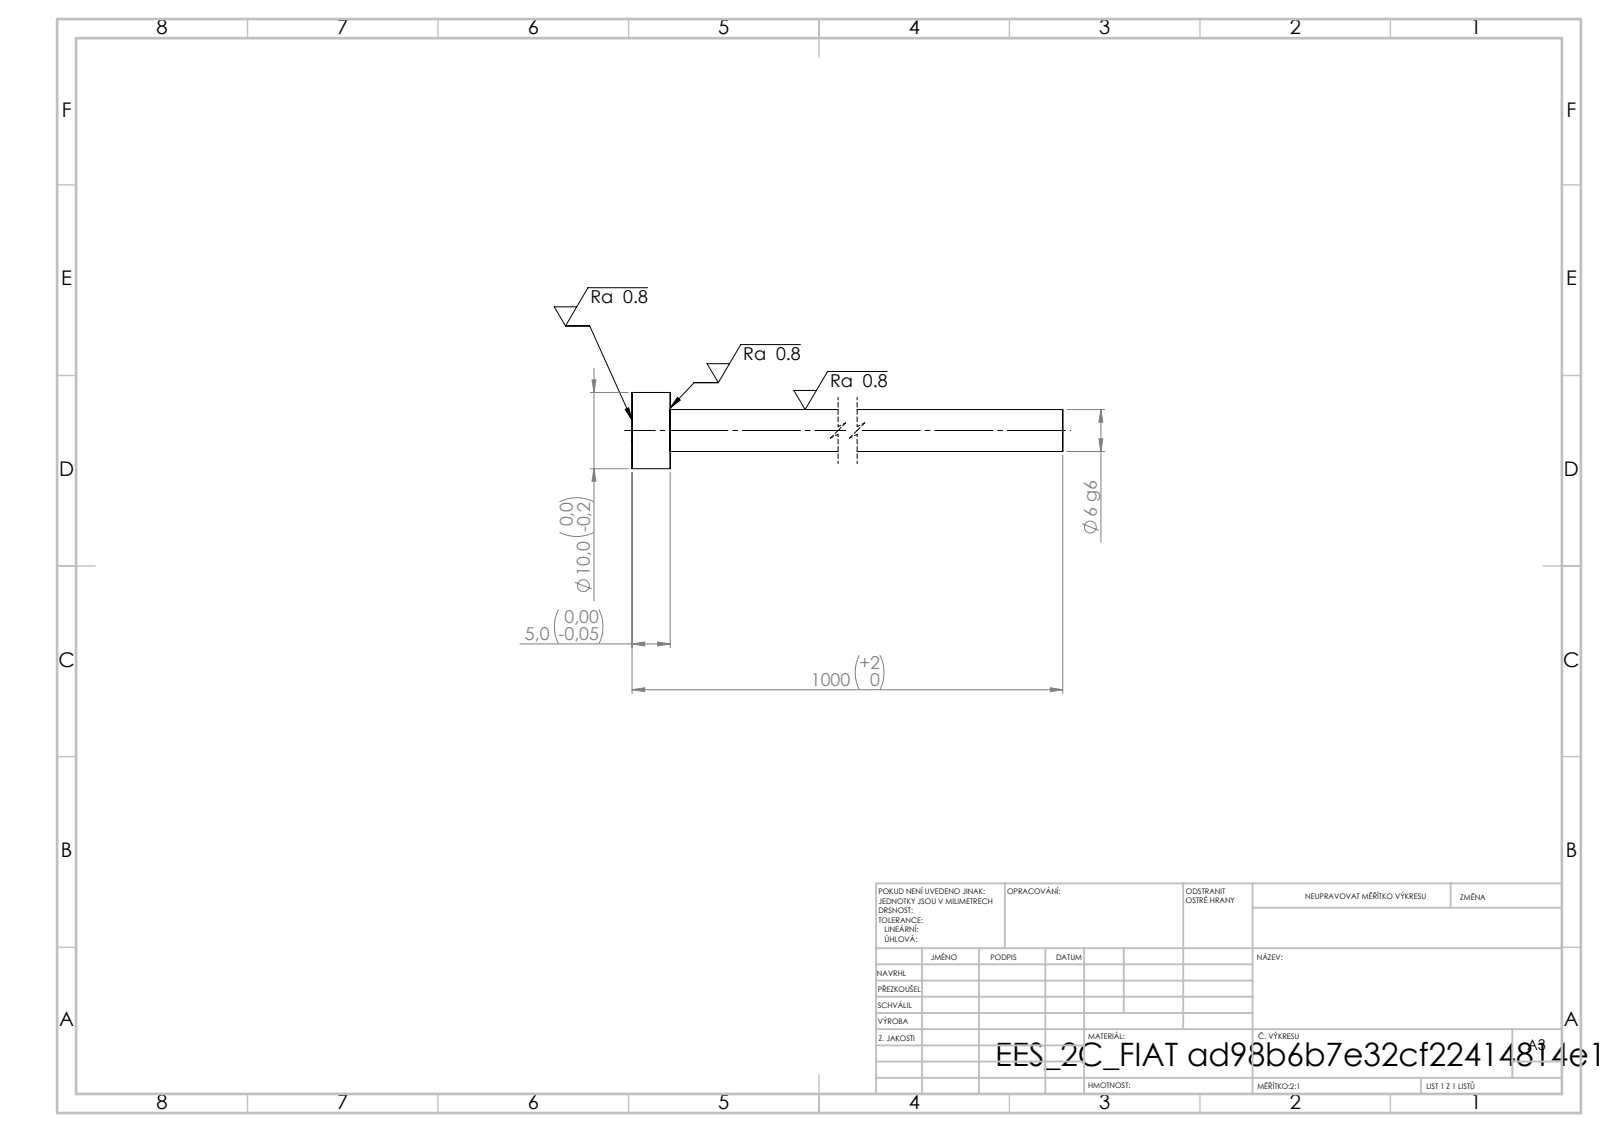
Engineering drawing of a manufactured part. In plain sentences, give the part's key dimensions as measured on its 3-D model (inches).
Its 3-D file was written by "SolidWorks 2019 (CONFIG_CONTROL_DESIGN)". It is 1 solid with 7 faces: 3 planar, 4 cylindrical and 0 other. Overall it measures 39.37 by 0.394 by 0.394 inches. Its volume is 1.467 cubic inches and its surface area 27.14 square inches. Round bosses or shafts: 1 of diameter 0.394, 1 of diameter 0.217. The main face-to-face distances are 0.197, 39.37, 39.173.
